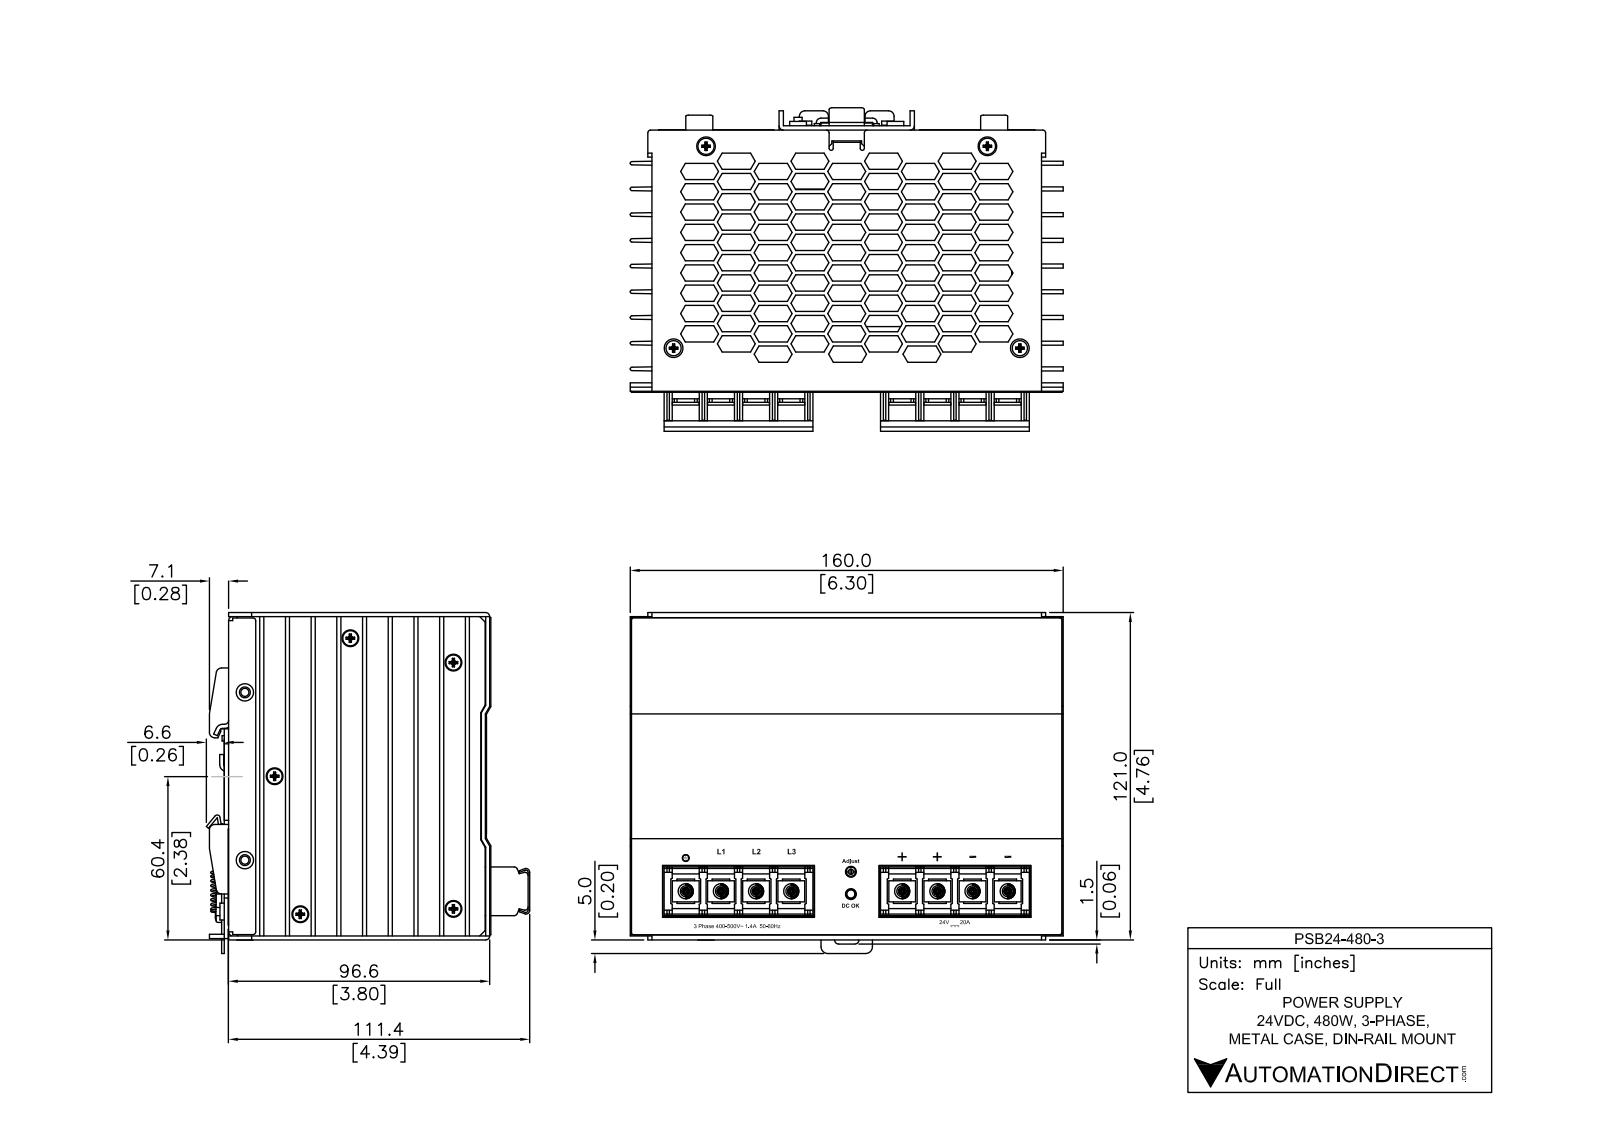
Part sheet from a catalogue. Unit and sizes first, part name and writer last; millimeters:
Units: millimetres
Overall size (bounding box): 160 × 125.6 × 117.1
Round holes (diameter × count): ⌀4.1 ×2
Round bosses / shafts (diameter × count): ⌀5.6 ×8, ⌀3.2 ×2
Partial cylindrical surfaces — rounded edges, fillets, slot ends (radius × count): R0.5 ×36, R0.8 ×22, R1.5 ×12, R1 ×3, R1.3 ×3, R1 ×2, R1.9 ×2, R2.3 ×2
Main face-to-face distances: 9.4, 1.9, 92.8, 90.9, 4.2, 92.1, 2.3, 88.6, 90.2, 87.9
Hole centre spacings: 10.2
Volume: 1 658 000 mm³ · Surface area: 221 700 mm²
Bodies: 1 solid, 2012 faces (1788 planar, 135 cylindrical, 89 other)
Part name (STEP PRODUCT): PSB24-480-3
STEP written by: SolidWorks 2011 (CONFIG_CONTROL_DESIGN)
